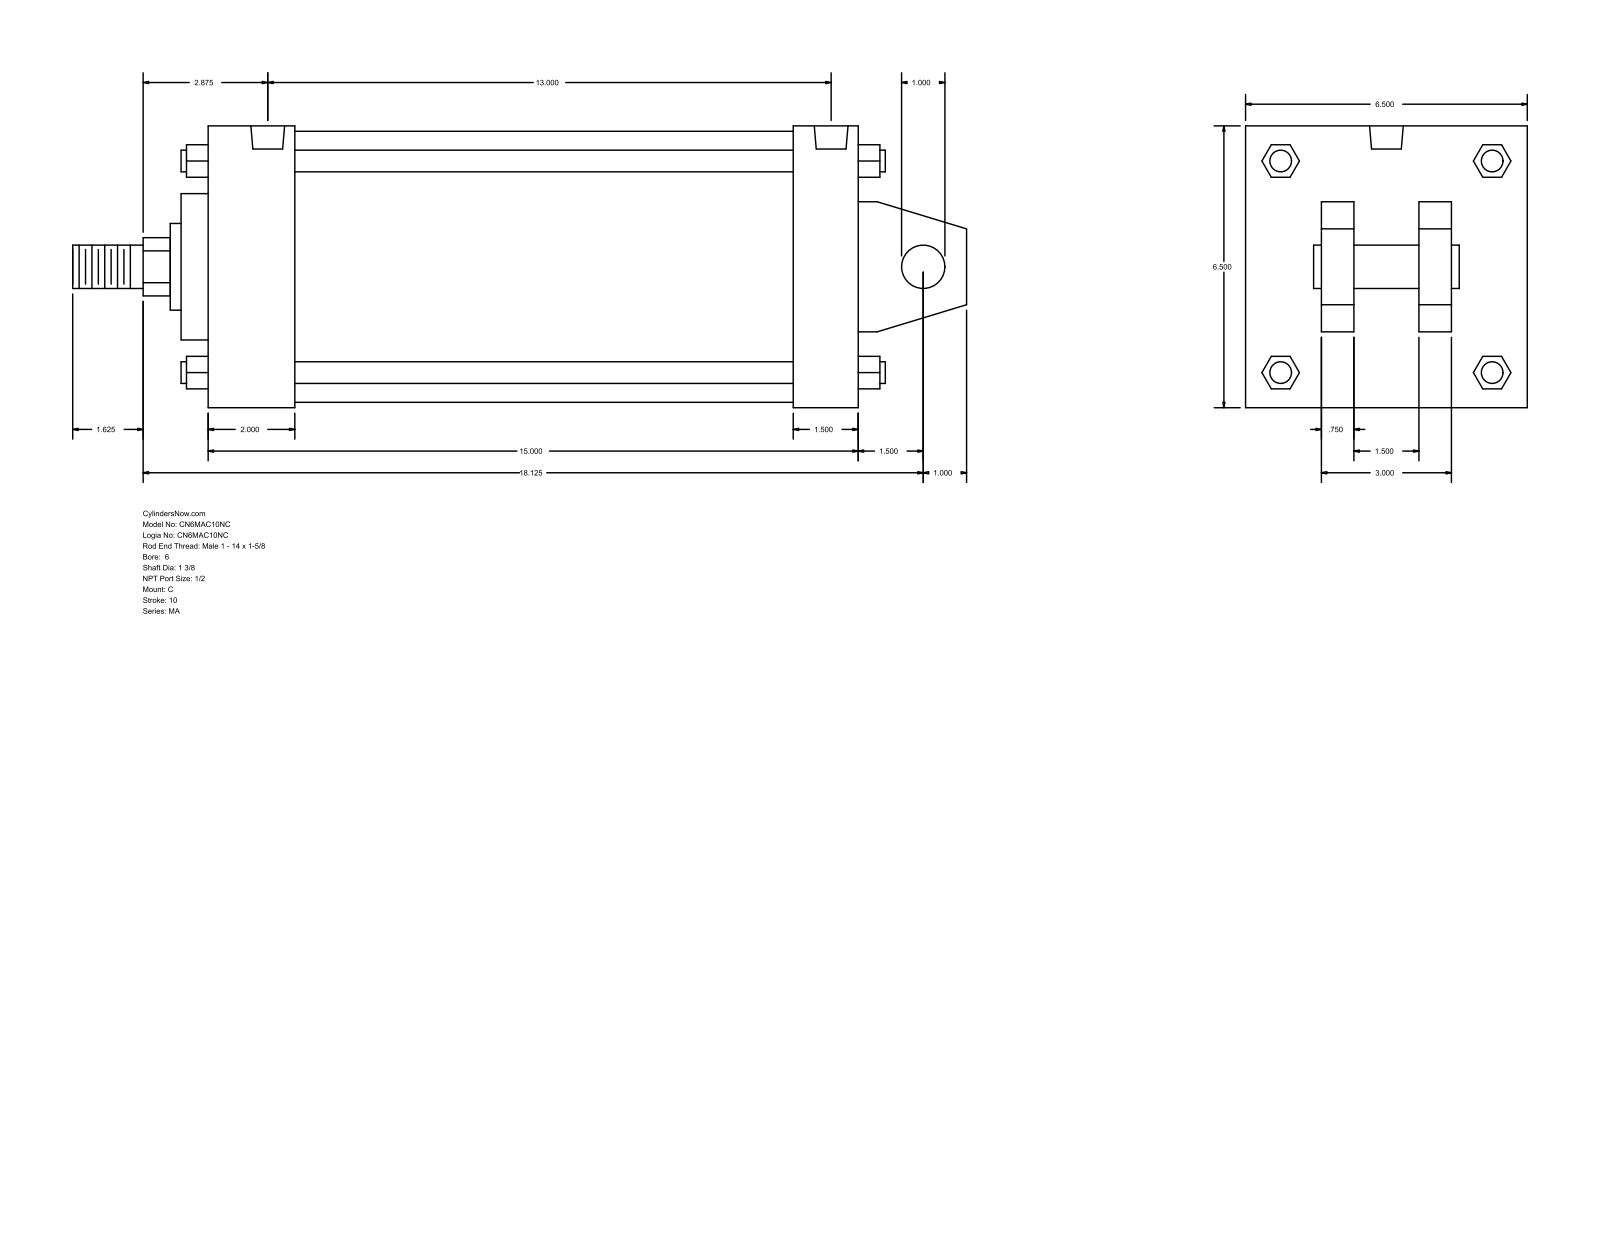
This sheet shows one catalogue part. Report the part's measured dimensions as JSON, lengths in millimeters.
{"part_name": "MA_C__0600_1.375", "step_written_by": "GSSL Pune (CONFIG_CONTROL_DESIGN)", "units": "millimeters", "bodies": {"solids": 0, "faces": 141, "planar": 109, "cylindrical": 32, "other": 0}, "overall_size": [523.88, 165.1, 165.1], "round_holes": [[17.46, 4], [19.77, 2]], "round_bosses_or_shafts": [[12.7, 4], [25.4, 2], [158.75, 1], [85.72, 1], [50.8, 1], [34.92, 1]], "partial_cylinders_radius": [[17.06, 1]], "face_to_face_distances": [165.1, 381, 38.1, 19.05, 63.5, 101.6, 50.8, 44.45, 120.65, 342.9], "hole_center_spacings": [330.2, 3.18, 327.02, 333.38]}
